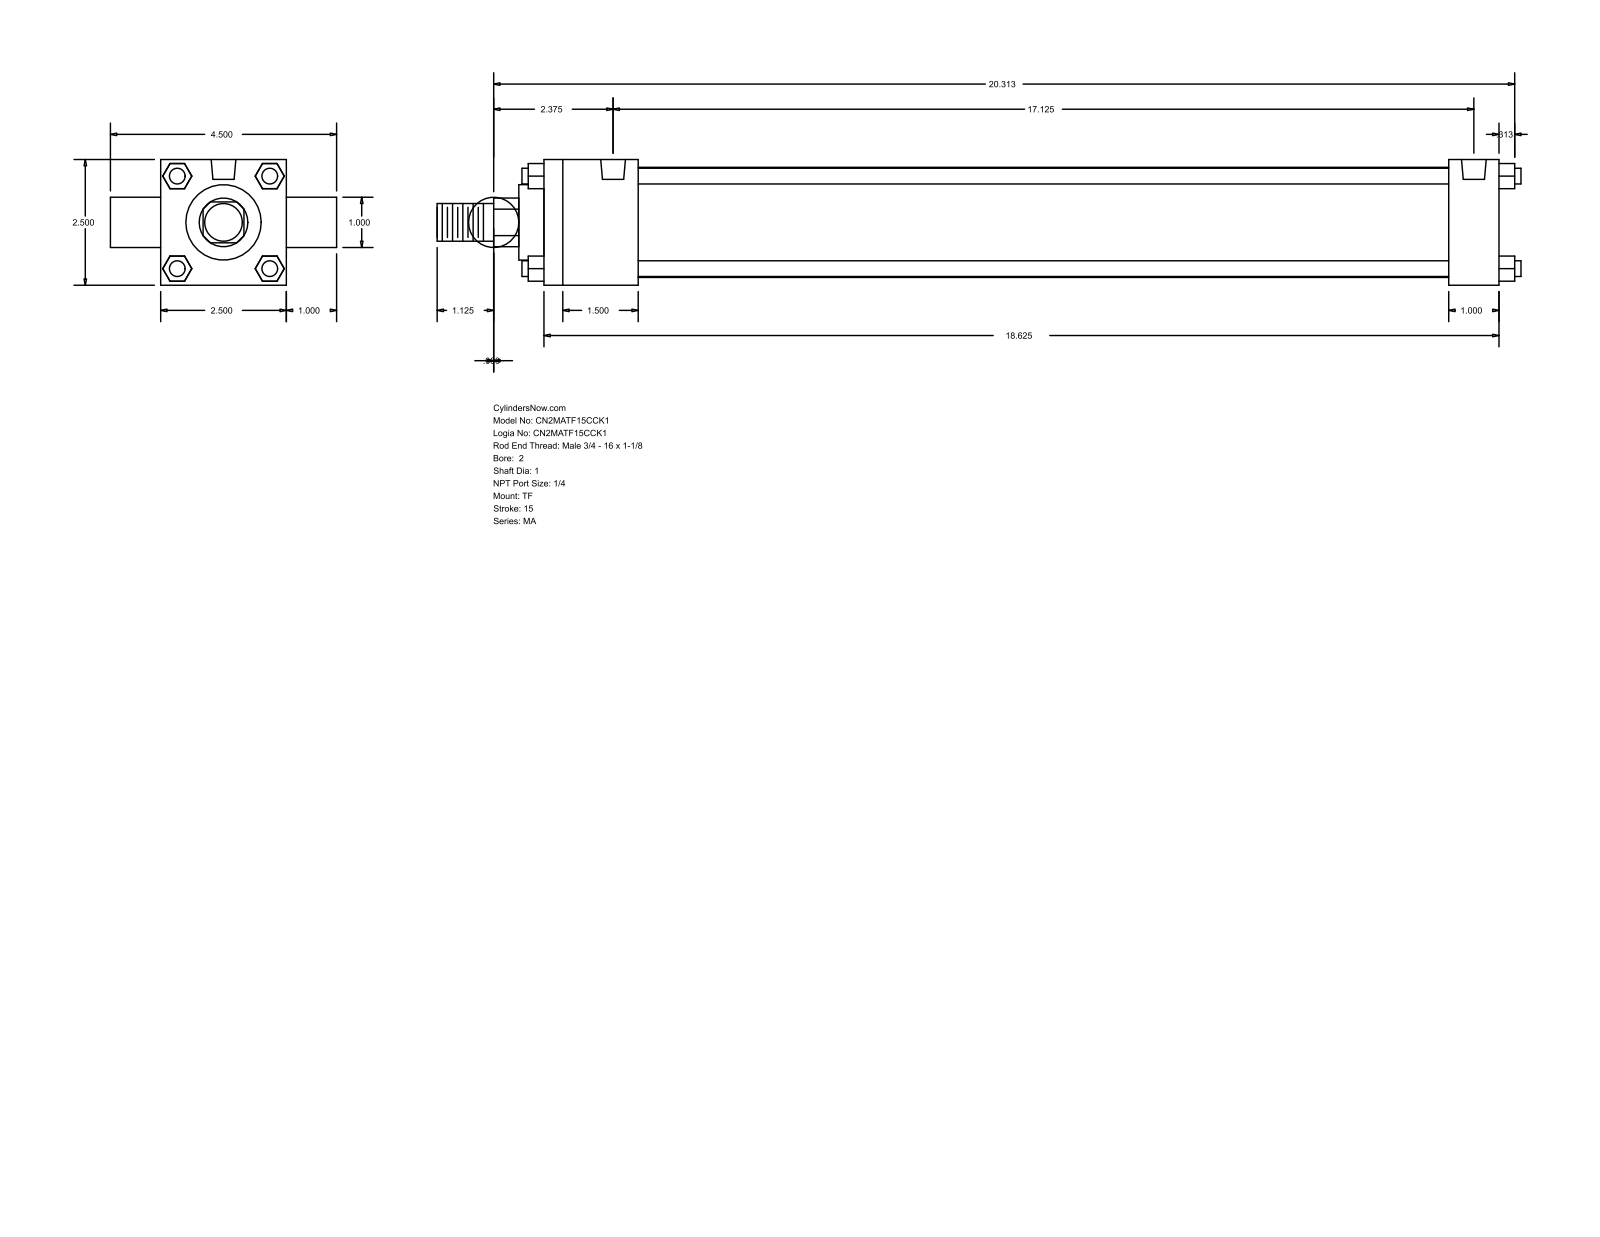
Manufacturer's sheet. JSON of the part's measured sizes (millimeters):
{"part_name": "MA_TF__0200_1", "step_written_by": "GSSL Pune (CONFIG_CONTROL_DESIGN)", "units": "millimeters", "bodies": {"solids": 0, "faces": 120, "planar": 92, "cylindrical": 28, "other": 0}, "overall_size": [547.69, 114.3, 63.5], "round_holes": [[7.94, 3], [12.49, 2]], "round_bosses_or_shafts": [[7.94, 4], [25.4, 2], [55.63, 1], [38.1, 1], [19.05, 1]], "partial_cylinders_radius": [[12.29, 1]], "face_to_face_distances": [63.5, 25.4, 482.6, 12.7, 47.63, 457.2, 409.57, 434.97, 88.9, 40.47], "hole_center_spacings": [434.97]}
